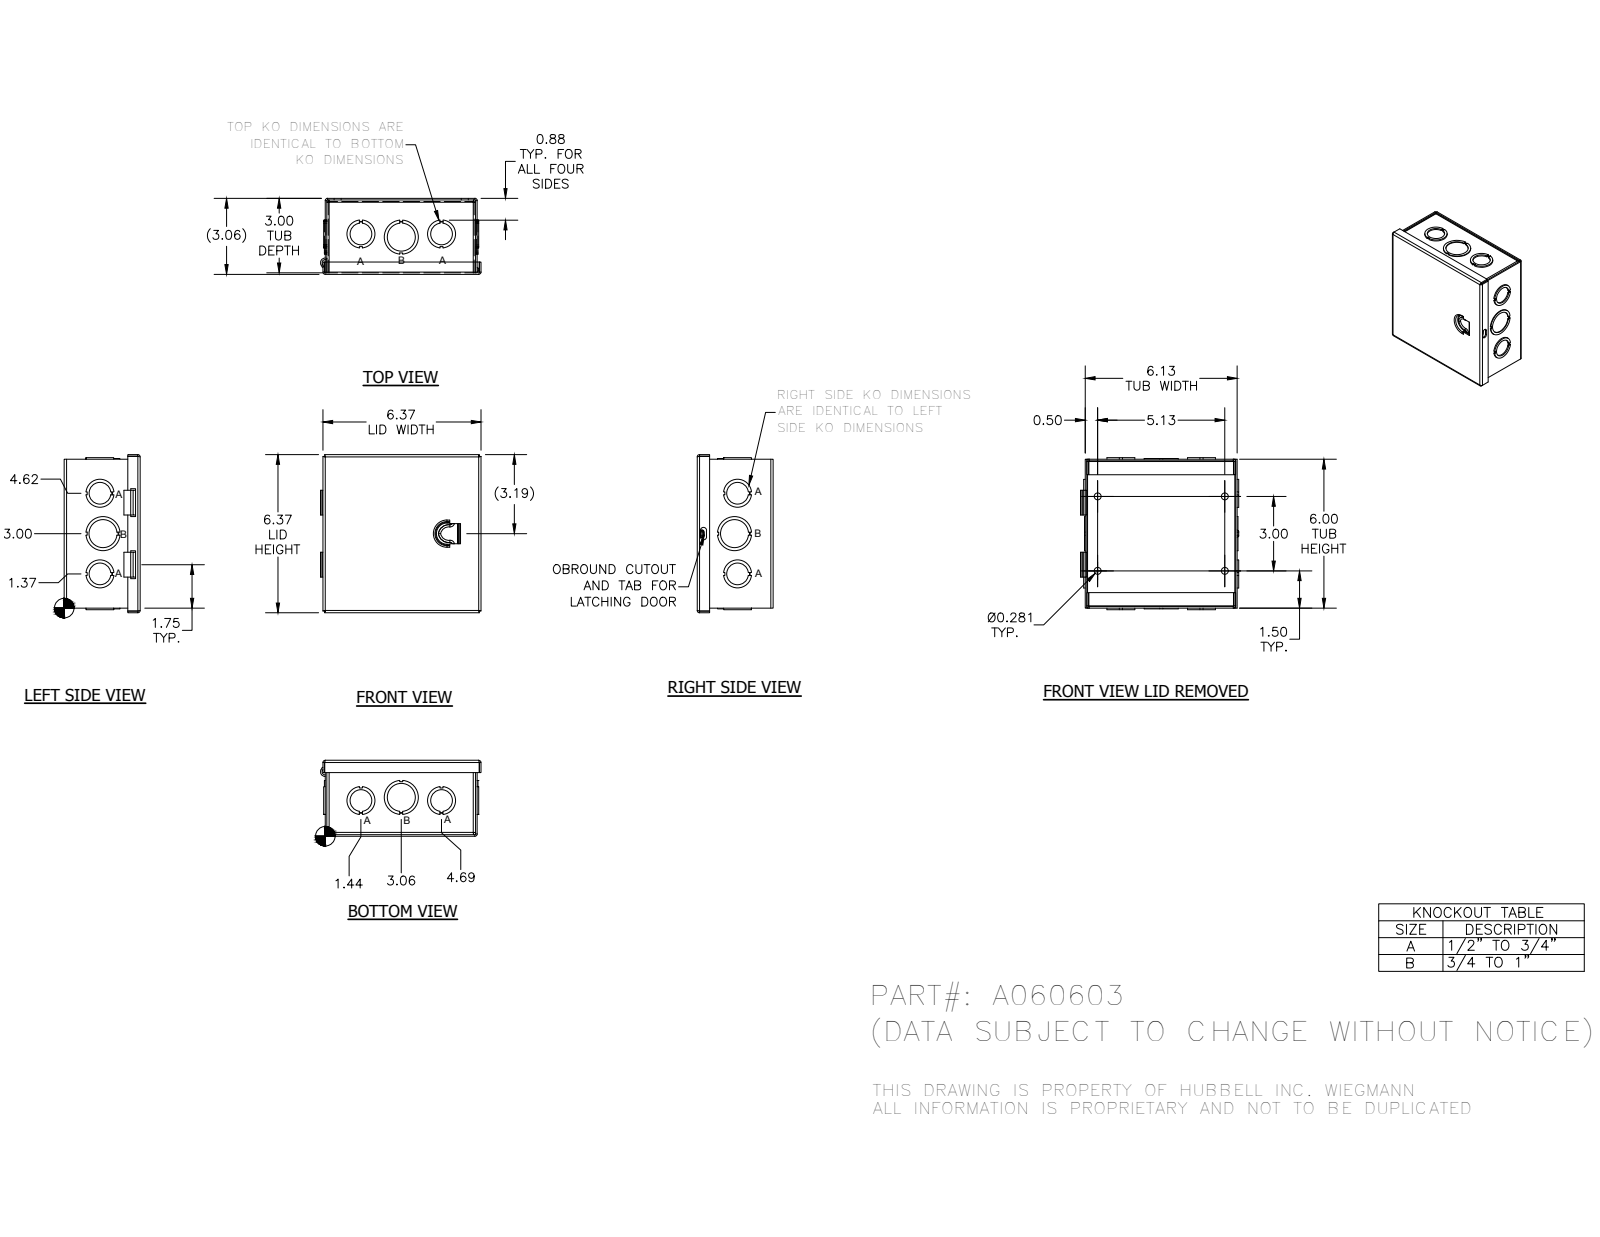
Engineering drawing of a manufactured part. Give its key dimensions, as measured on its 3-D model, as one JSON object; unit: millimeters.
{"part_name": "A060603BLR; A0603TB; A0606LFA; 35010 (+1 more)", "step_written_by": "Autodesk Inventor 2014 (AUTOMOTIVE_DESIGN)", "units": "millimeters", "bodies": {"solids": 20, "faces": 555, "planar": 391, "cylindrical": 129, "other": 35}, "overall_size": [165.95, 163.49, 77.79], "round_holes": [[28.57, 8], [22.22, 6], [7.14, 4], [34.92, 2]], "partial_cylinders_radius": [[0.79, 18], [2.38, 8], [3.17, 7], [0.79, 4], [2.37, 4], [1.59, 3], [1.54, 1], [3.2, 1]], "face_to_face_distances": [1.59, 1.58, 152.4, 74.62, 76.2, 150.81, 76.21, 77.79, 153.99, 155.58], "hole_center_spacings": [41.39, 41.4, 82.55, 76.2, 130.18, 150.84, 82.54, 82.56]}
